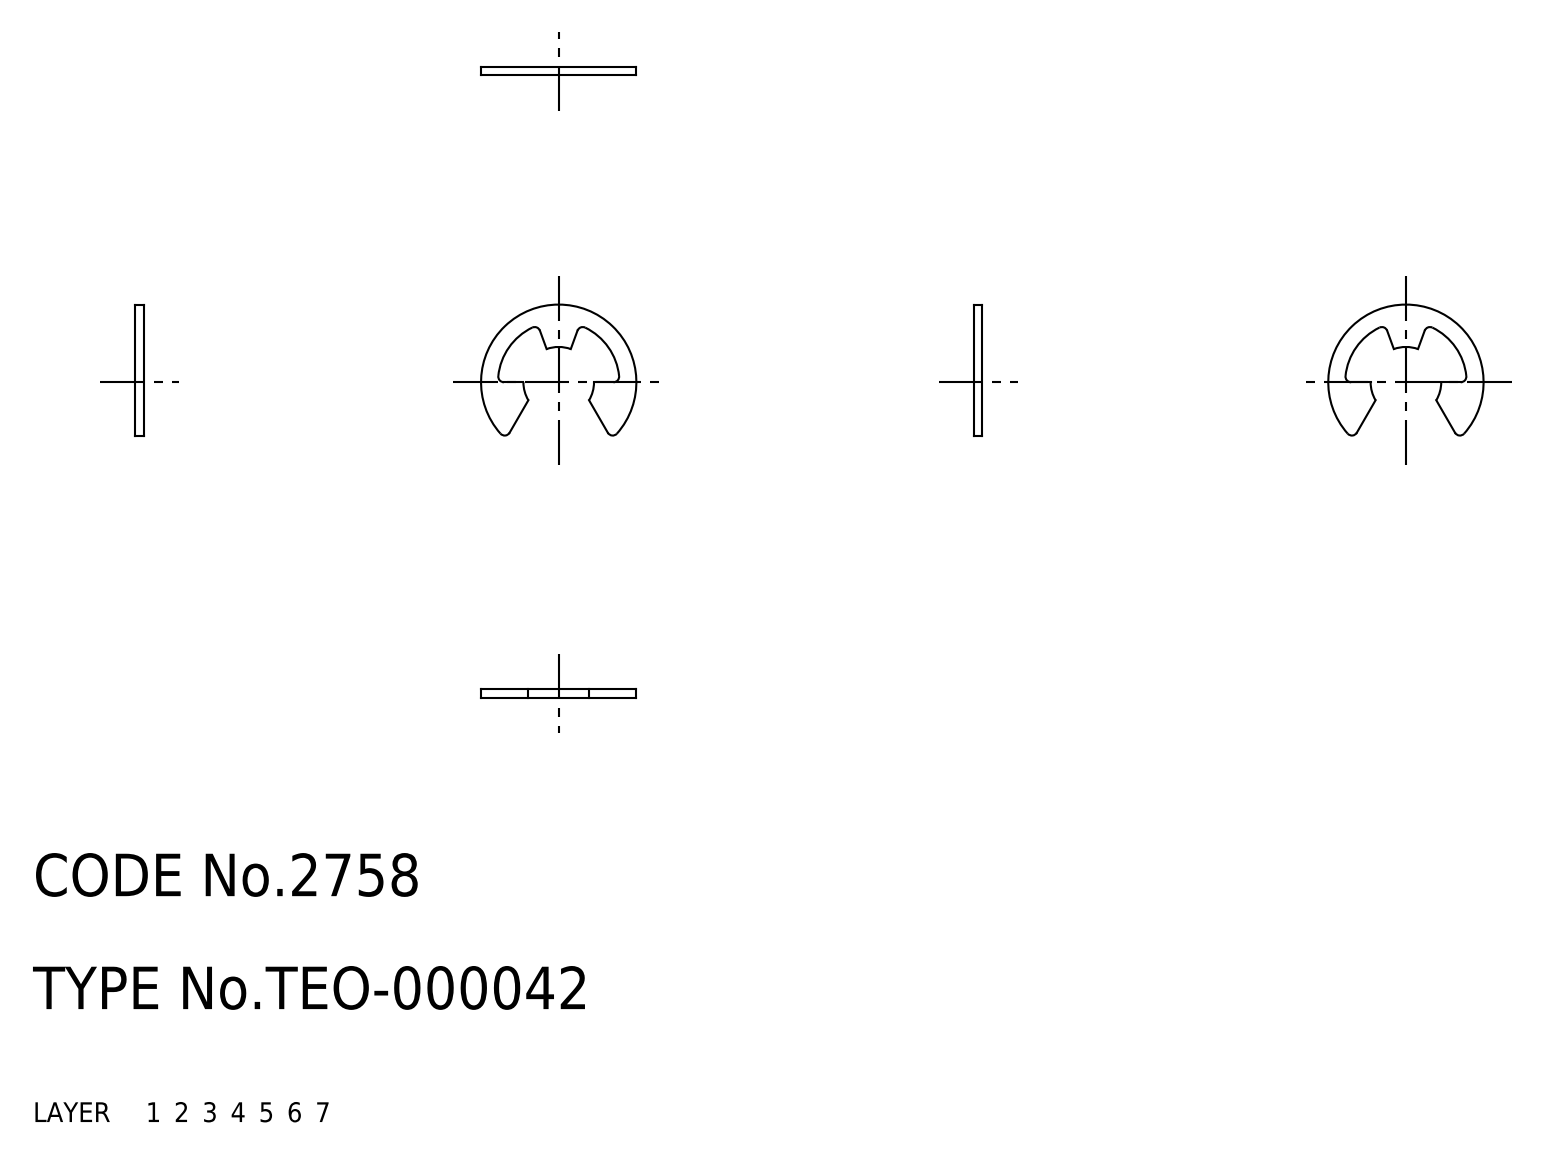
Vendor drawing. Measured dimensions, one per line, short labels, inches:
name: retainer
written by: CADfix (AUTOMOTIVE_DESIGN)
unit: in
bodies: 1 solid, 20 faces (0 planar, 0 cylindrical, 20 other)
size: 0.433 × 0.365 × 0.024
volume: 0.001 in³; area: 0.175 in²
